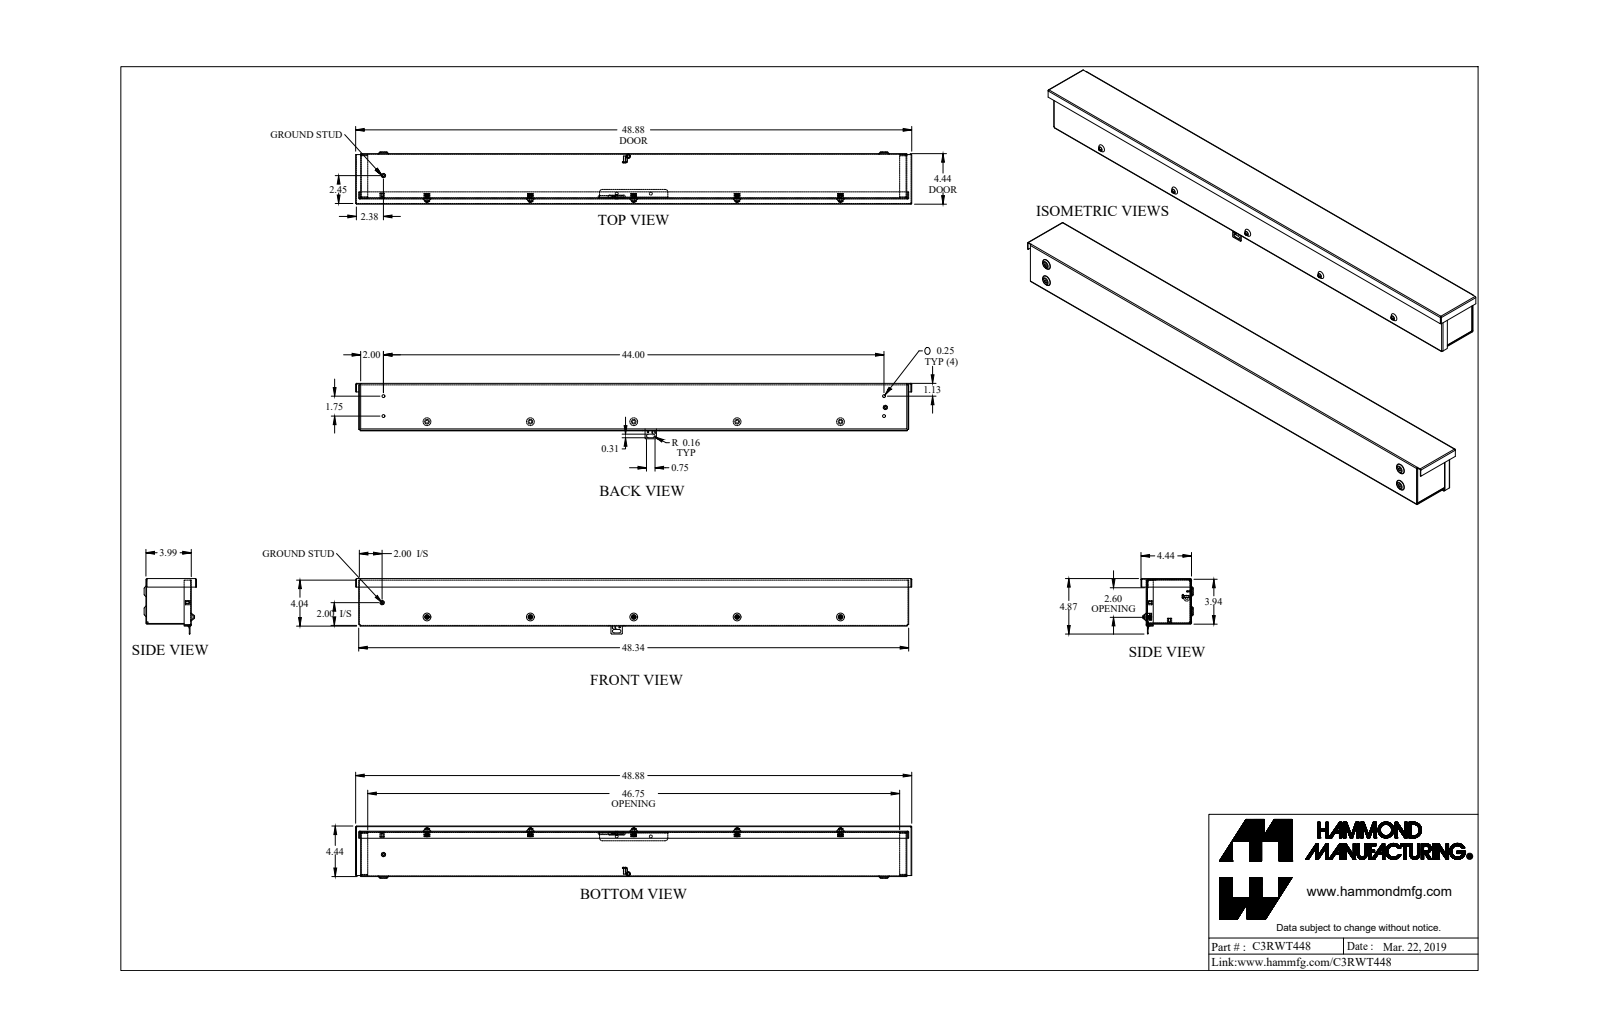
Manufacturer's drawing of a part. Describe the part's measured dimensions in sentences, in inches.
The part is named "C3RWT448_Default". Its 3-D file was written by "SolidWorks 2019 (CONFIG_CONTROL_DESIGN)". It is 28 solids with 1008 faces: 557 planar, 315 cylindrical and 136 other. Overall it measures 48.875 by 4.871 by 4.594 inches. Its volume is 54.64 cubic inches and its surface area 1 935 square inches. Round holes: 7 of diameter 0.156, 6 of diameter 0.25, 5 of diameter 0.214, 5 of diameter 0.23, 2 of diameter 0.203, 1 of diameter 0.125, 1 of diameter 0.137, 1 of diameter 0.2, 1 of diameter 0.215. Round bosses or shafts: 6 of diameter 0.19, 5 of diameter 0.148, 2 of diameter 0.375, 1 of diameter 0.5, 1 of diameter 0.367, 1 of diameter 0.21, 1 of diameter 0.152, 1 of diameter 0.125. Partial cylindrical surfaces (rounded edges, fillets, slot ends): 20 of radius 0.08, 20 of radius 0.108, 18 of radius 0.029, 18 of radius 0.086, 15 of radius 0.125, 10 of radius 0.022, 6 of radius 0.25, 5 of radius 0.171. The main face-to-face distances are 0.057, 3.943, 3.928, 3.871, 3.886, 3.985, 4, 4.381, 0.51, 0.453. The hole center spacings are 9.086, 9.086, 18.172, 27.258, 2.901, 6.674, 12.924, 13.109.
